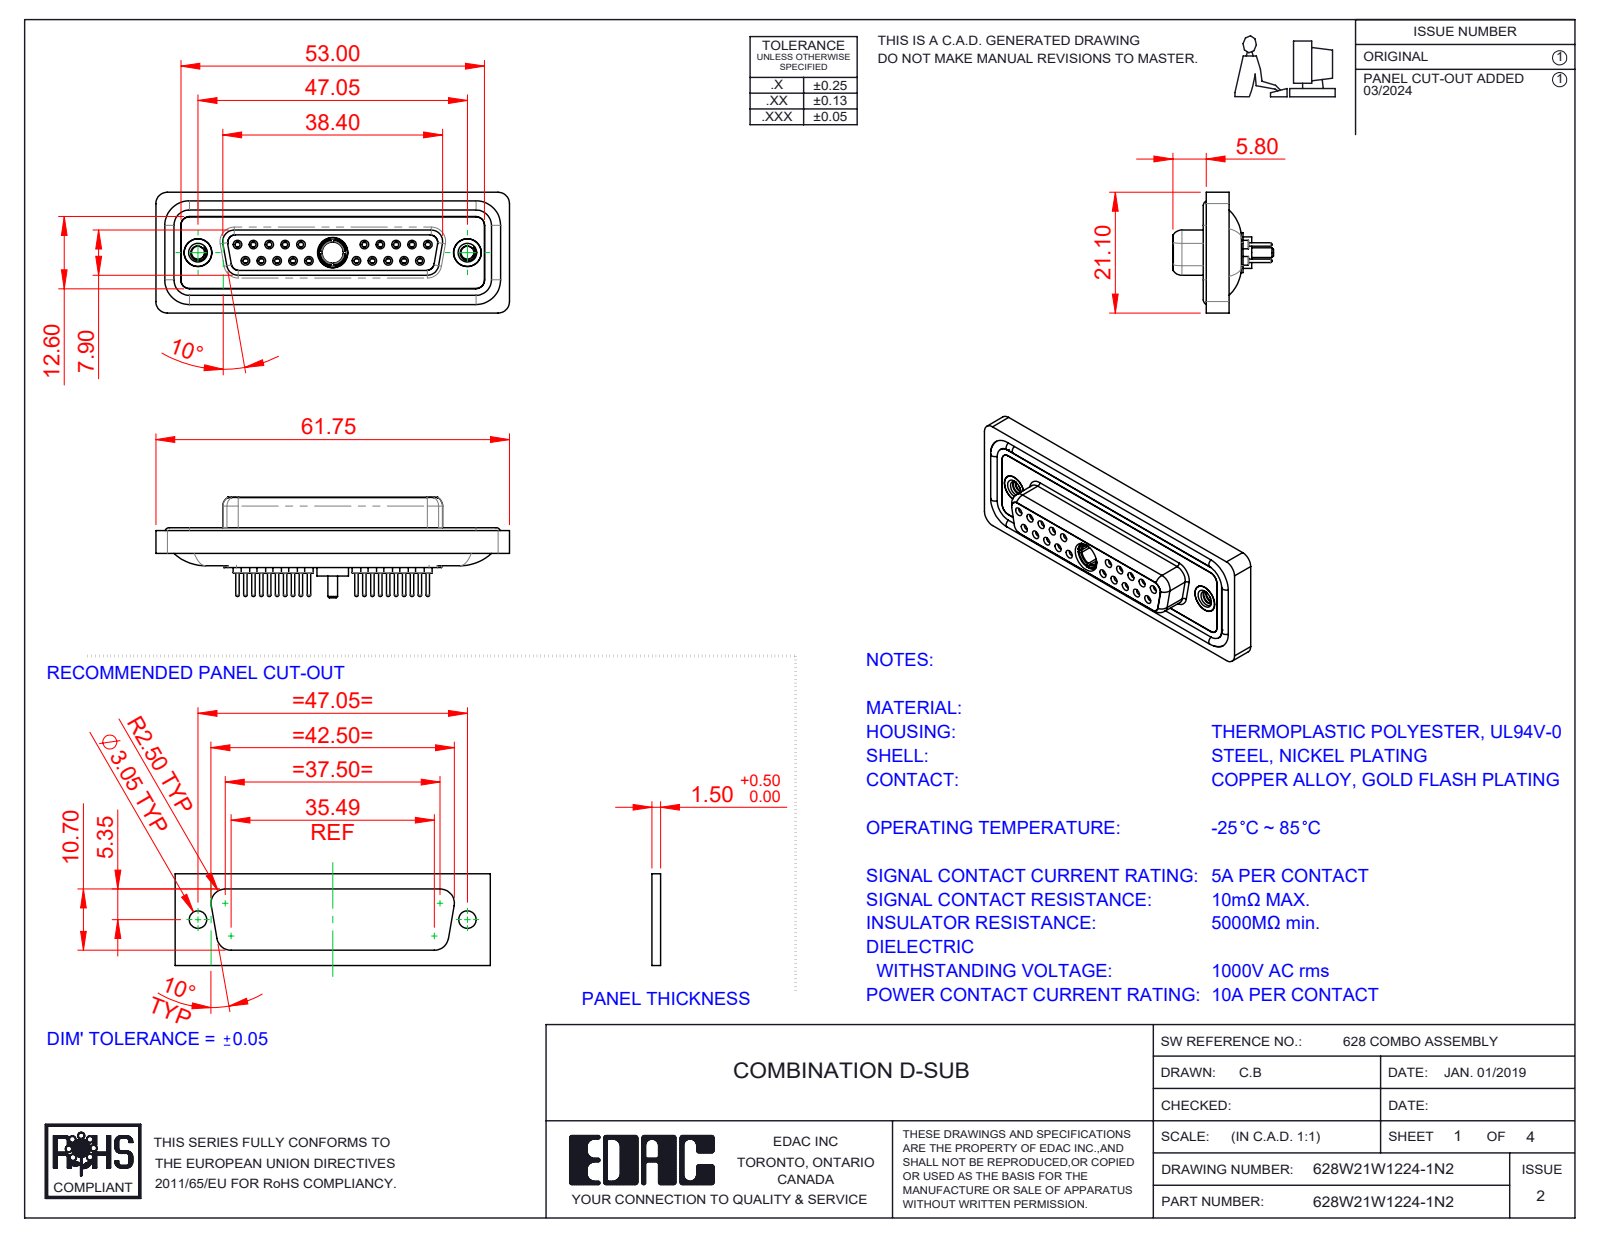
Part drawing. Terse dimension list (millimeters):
name: 628Combo Housing_21W1; Power Socket_10A S; 628W21W1224-1N2; 628Combo Contact Row 2_24 (+5 more)
written by: SolidWorks 2023 (CONFIG_CONTROL_DESIGN)
unit: mm
bodies: 29 solids, 1560 faces (434 planar, 591 cylindrical, 535 other)
size: 61.75 × 21.1 × 17.55
volume: 8 359 mm³; area: 13 989 mm²
holes: 20× ⌀0.9, 20× ⌀1.1, 20× ⌀1.5, 20× ⌀2, 10× ⌀1.6, 10× ⌀1.7, 3× ⌀4.85, 2× ⌀2.26, 2× ⌀4, 2× ⌀4.05, 2× ⌀5, 1× ⌀3.7
bosses: 20× ⌀2.2, 20× ⌀0.6, 14× ⌀1.6, 2× ⌀4.95, 2× ⌀4.8, 1× ⌀5.5, 1× ⌀5.2, 1× ⌀4.96
rounds: 22× R1.5, 18× R2, 8× R1.35, 8× R1.6, 4× R0.25, 4× R0.5, 4× R0.6, 4× R0.65
face distances: 0.4, 1.8, 7.45, 6.6, 5.65, 0.5, 1.6, 7.05, 2.9, 1.1
hole spacings: 3.16, 2.77, 5.54, 5.03, 8.31, 7.48, 16.62, 19.39
